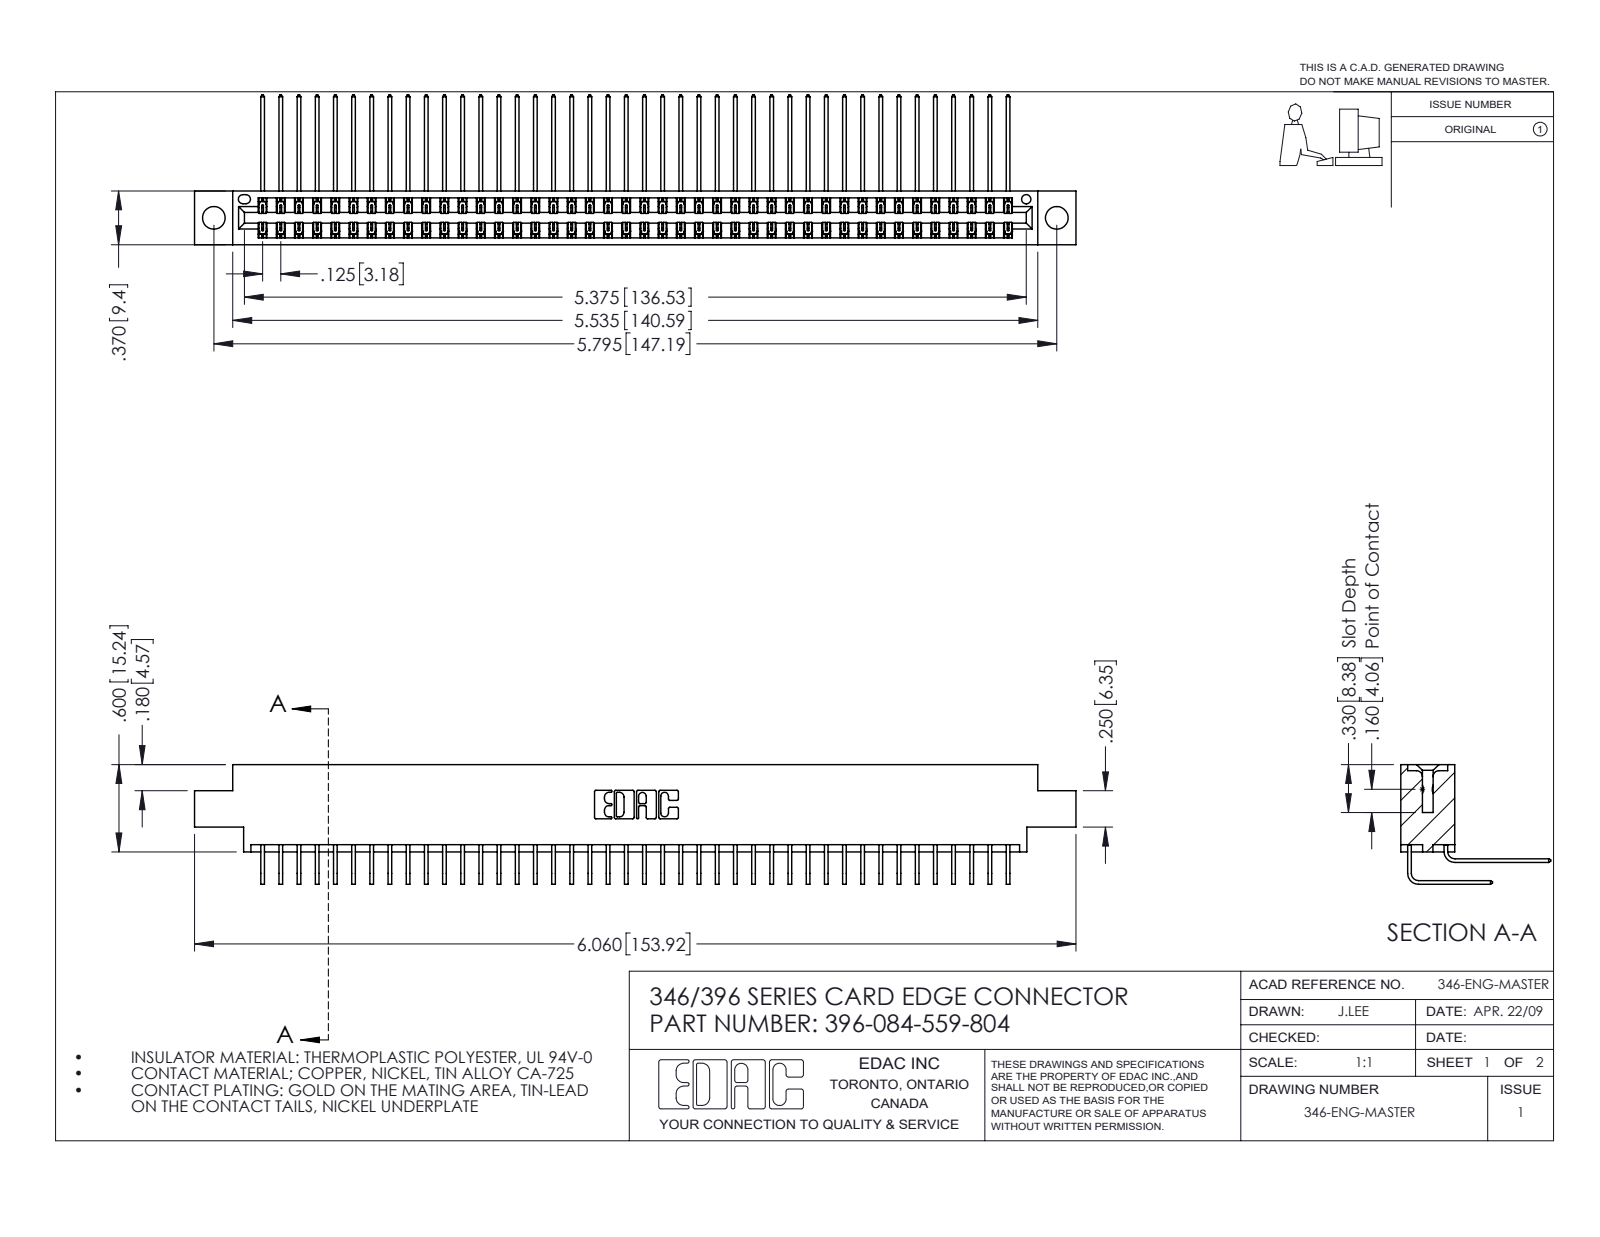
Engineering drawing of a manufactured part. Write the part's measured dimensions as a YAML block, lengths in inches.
part_name: "345-292-001_559 Tail - 2; 345-292-001_558 559 Tail - 1; 346 Part_0.170 Offset - 0.156 Dia-TH; 396-084-559-804"
step_written_by: "SolidWorks 2016 (CONFIG_CONTROL_DESIGN)"
units: inches
bodies: {solids: 85, faces: 4662, planar: 3188, cylindrical: 1474, other: 0}
overall_size: [6.06, 1.03, 0.823]
volume: 0.931
surface_area: 36.09
round_holes:
  - {diameter: 0.156, count: 2}
  - {diameter: 0.064, count: 1}
partial_cylinders:
  - {radius: 0.006, count: 126}
  - {radius: 0.01, count: 22}
  - {radius: 0.007, count: 6}
  - {radius: 0.031, count: 6}
  - {radius: 0.026, count: 3}
  - {radius: 0.014, count: 2}
  - {radius: 0.022, count: 2}
  - {radius: 0.024, count: 2}
face_to_face_distances: [0.048, 0.322, 0.025, 0.37, 0.25, 0.072, 0.298, 0.275, 0.148, 0.222]
hole_center_spacings: [0.246, 5.586, 5.795]
